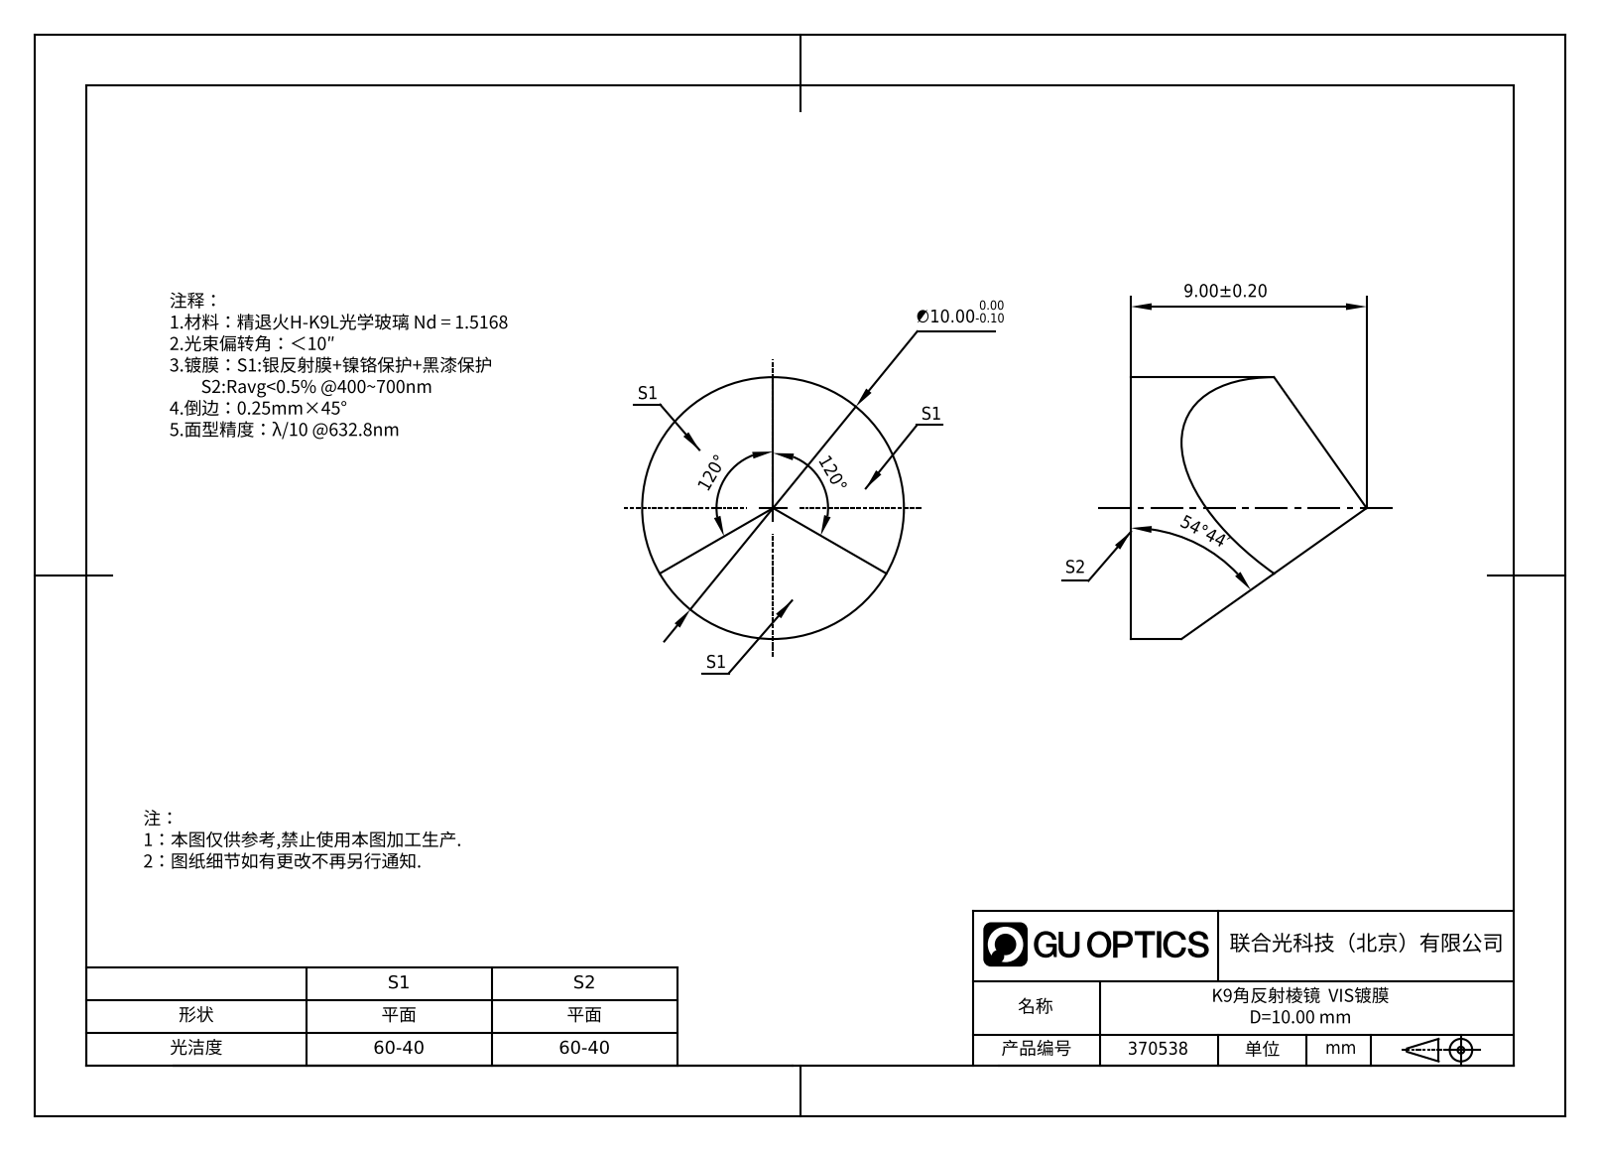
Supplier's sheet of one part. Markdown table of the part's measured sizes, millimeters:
| quantity | value |
| --- | --- |
| part name | GP16-010-2 |
| STEP written by | SolidWorks 2022 (AUTOMOTIVE_DESIGN) |
| units | millimeters |
| bodies | 1 solid, 12 faces (8 planar, 2 cylindrical, 2 other) |
| overall size | 10 × 10 × 8.88 |
| volume | 400 mm³ |
| surface area | 311 mm² |
| round bosses / shafts (diameter × count) | 10 × 1 |
| main face-to-face distances | 8.88 |
